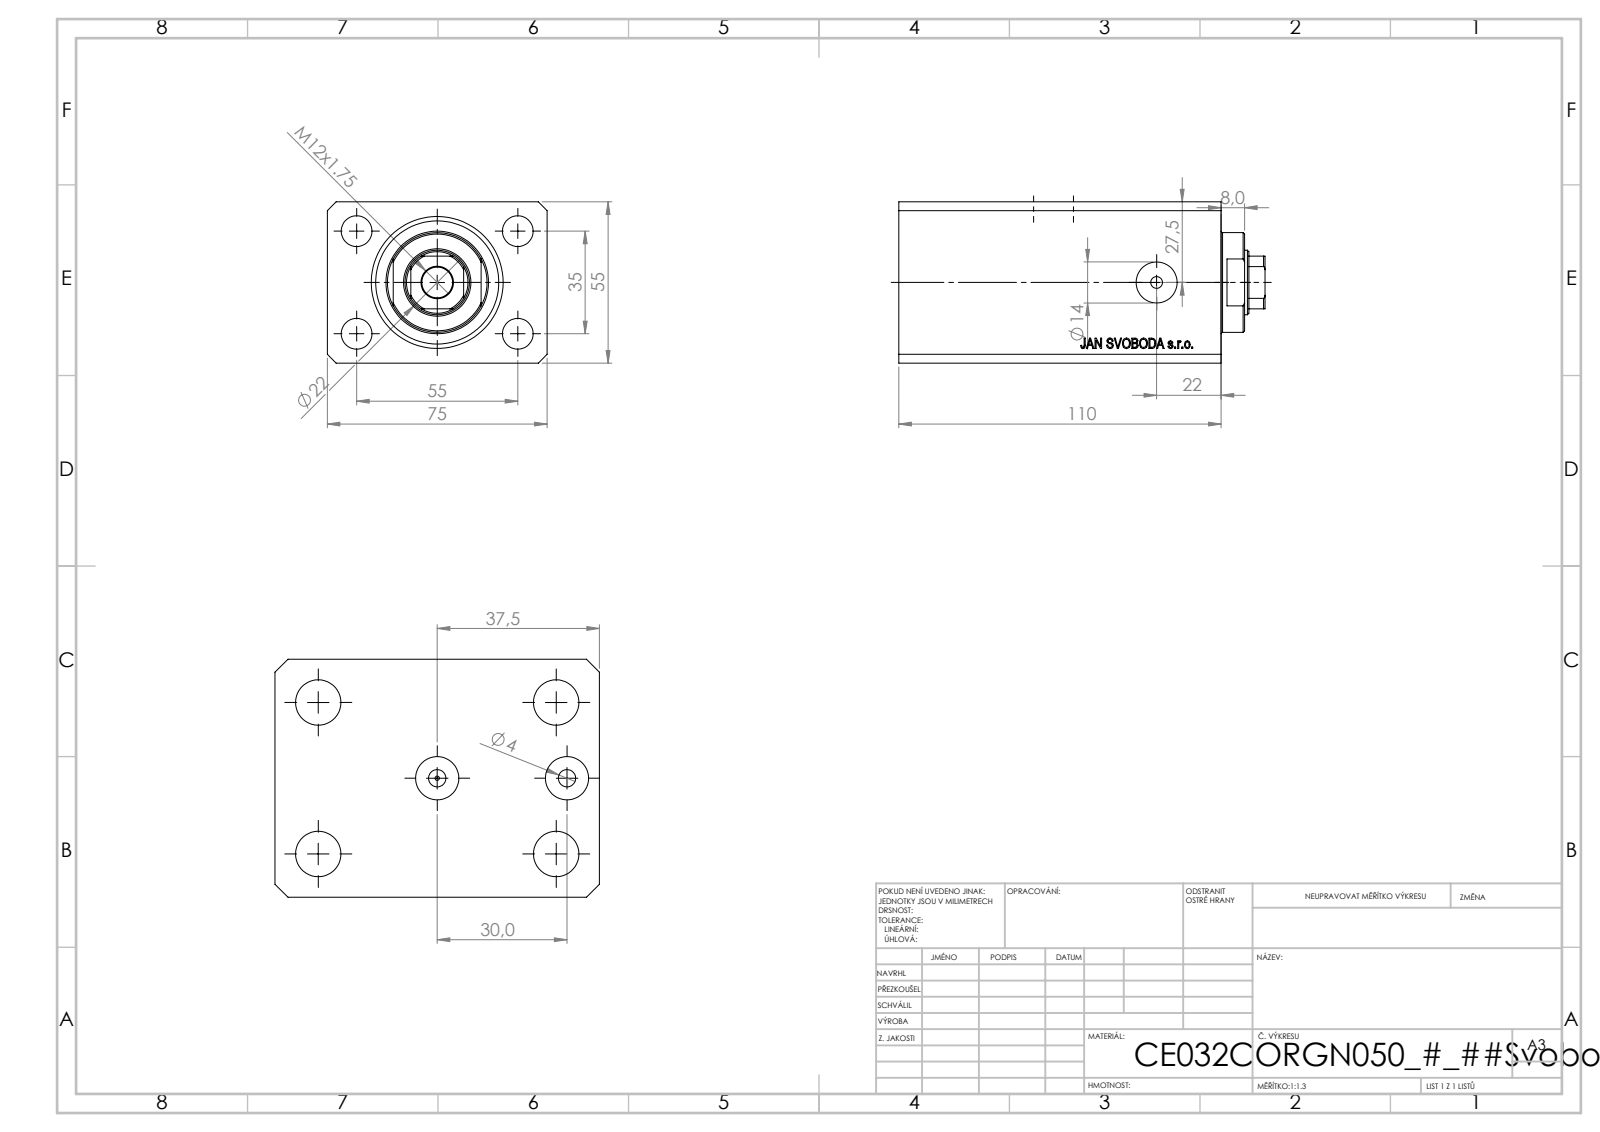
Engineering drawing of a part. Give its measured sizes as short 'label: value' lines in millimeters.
name: V250CE_C_VCP; V250CE_C_Body; V250CE_VC_C
written by: SolidWorks 2019 (CONFIG_CONTROL_DESIGN)
unit: mm
bodies: 3 solids, 868 faces (428 planar, 46 cylindrical, 394 other)
size: 125 × 75 × 55
volume: 396 222 mm³; area: 81 355 mm²
holes: 5× ⌀10.5, 4× ⌀4, 2× ⌀10, 2× ⌀14, 1× ⌀1.25, 1× ⌀22, 1× ⌀32, 1× ⌀45
bosses: 1× ⌀34
rounds: 1× R10.5
face distances: 55, 75, 110, 15, 95, 9.9, 85.1, 100.1, 87.66, 8
hole spacings: 32.6, 17.68, 35, 55, 60.1, 65.19, 30, 66
